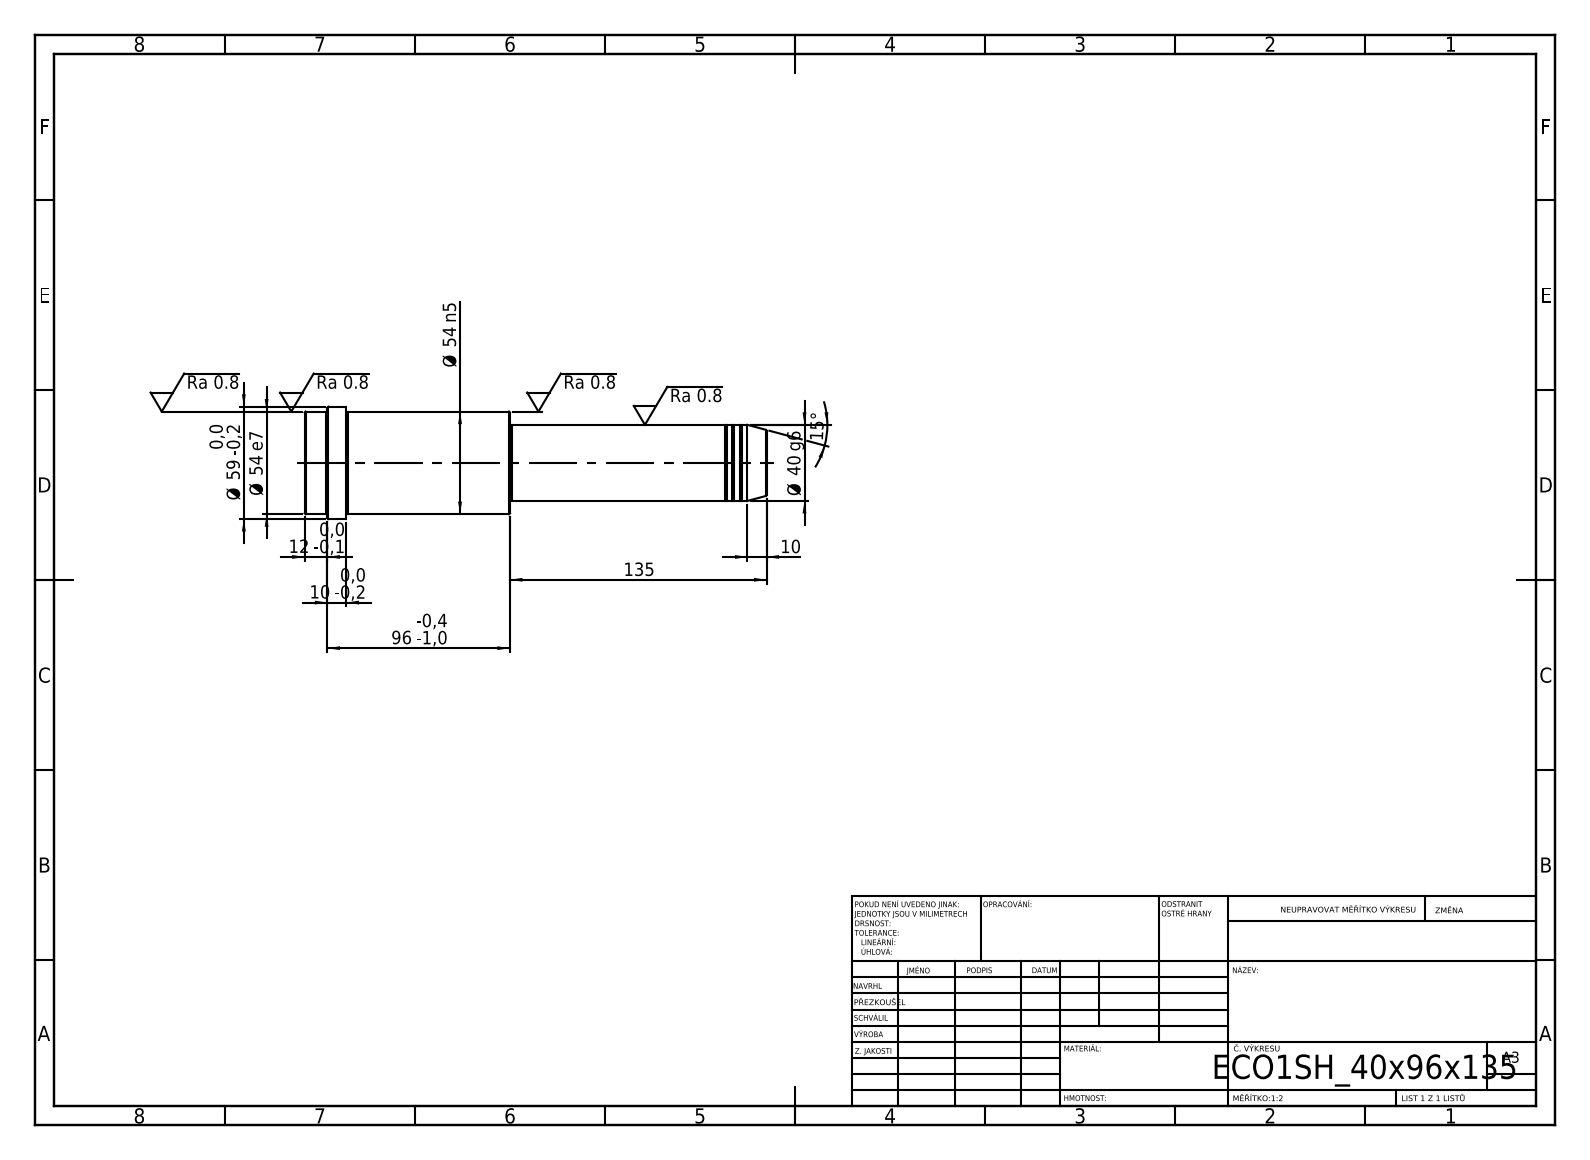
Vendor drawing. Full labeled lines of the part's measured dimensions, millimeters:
STEP written by: SolidWorks 2019 (CONFIG_CONTROL_DESIGN)
Units: millimetres
Bodies: 1 solid, 52 faces (6 planar, 16 cylindrical, 30 other)
Overall size (bounding box): 243 × 59 × 59
Volume: 419 410 mm³ · Surface area: 40 902 mm²
Round bosses / shafts (diameter × count): ⌀59 ×1, ⌀54 ×1, ⌀40 ×1, ⌀39 ×1
Main face-to-face distances: 108, 135, 243, 221, 86, 22, 231, 96, 10, 12
